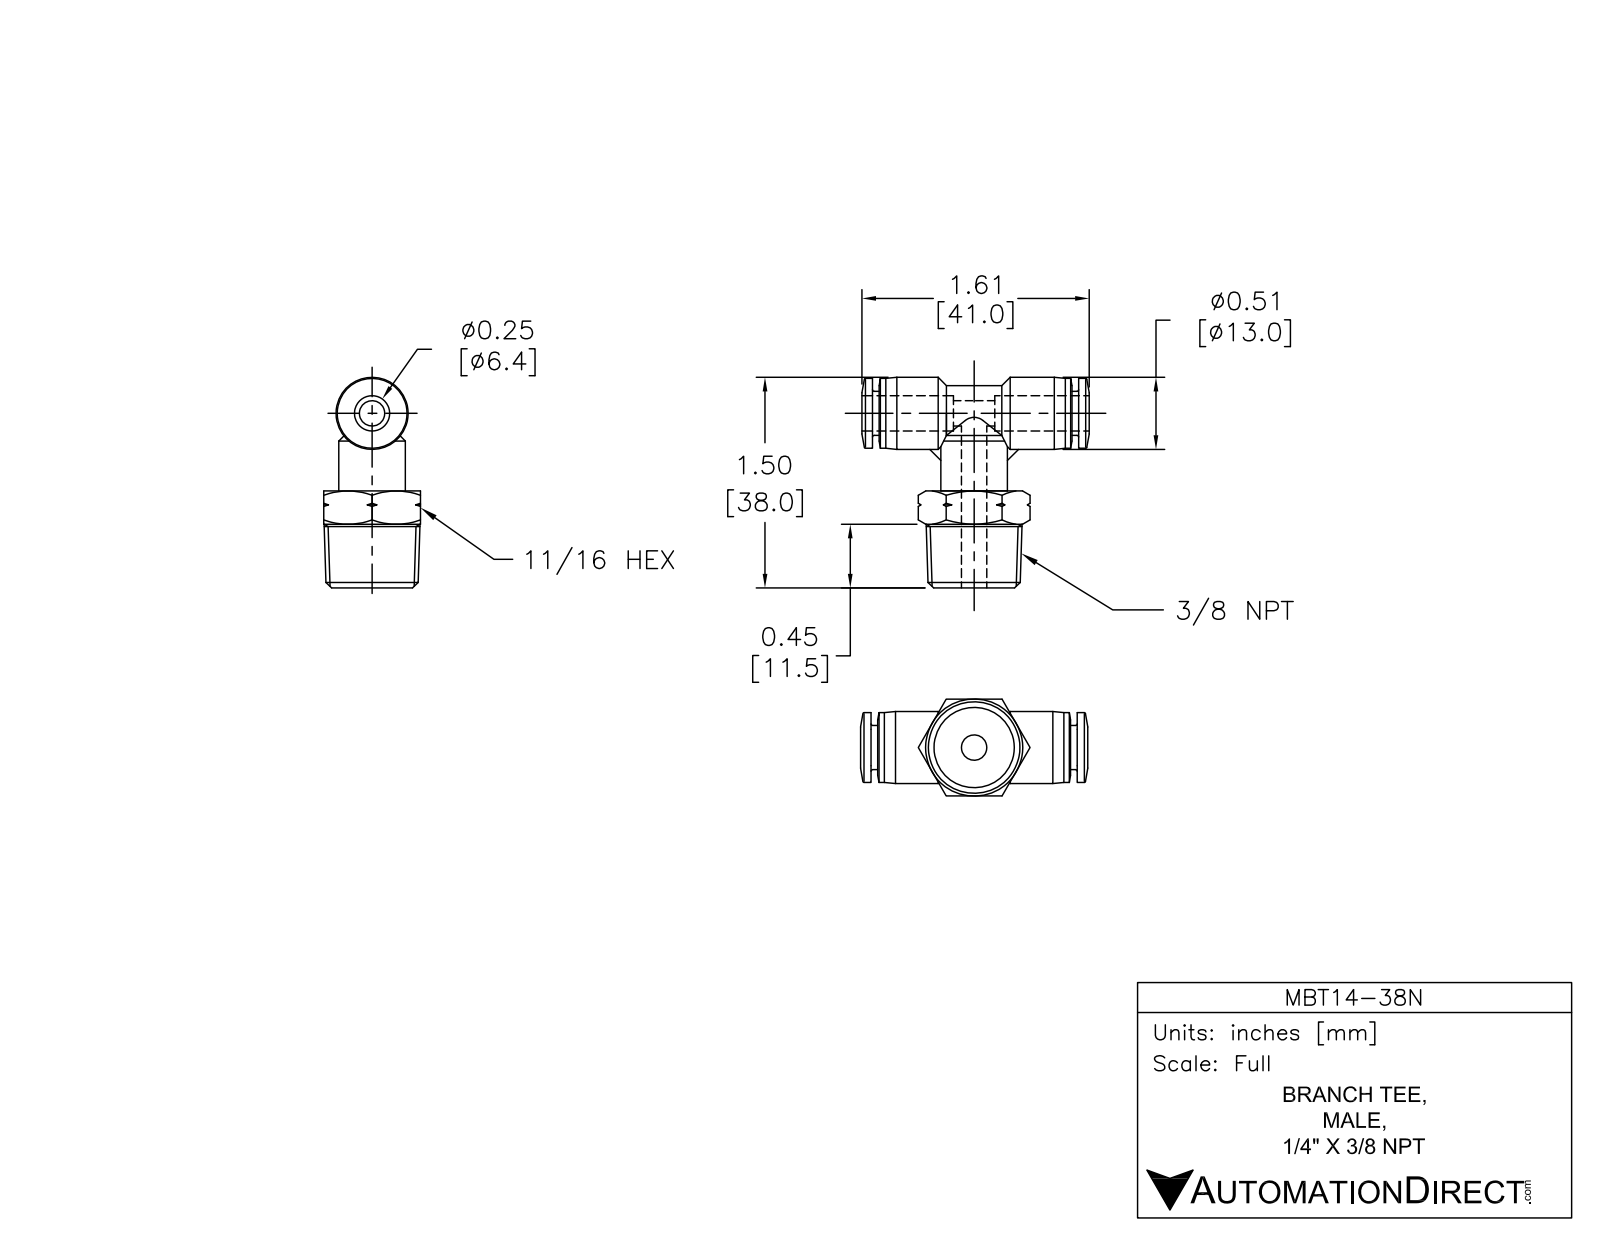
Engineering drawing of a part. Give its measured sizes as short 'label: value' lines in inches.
name: MBT14-38N
written by: SolidWorks 2015 (AUTOMOTIVE_DESIGN)
unit: in
bodies: 1 solid, 118 faces (21 planar, 31 cylindrical, 66 other)
size: 1.614 × 1.496 × 0.687
volume: 0.489 in³; area: 7.446 in²
holes: 2× ⌀0.177, 1× ⌀0.258
bosses: 1× ⌀0.512, 1× ⌀0.496, 1× ⌀0.472, 1× ⌀0.394, 1× ⌀0.313
rounds: 1× R0.197
face distances: 0.687, 0.689, 1.465, 0.047, 1.417, 0.587, 0.878, 0.539, 0.831, 1.37
